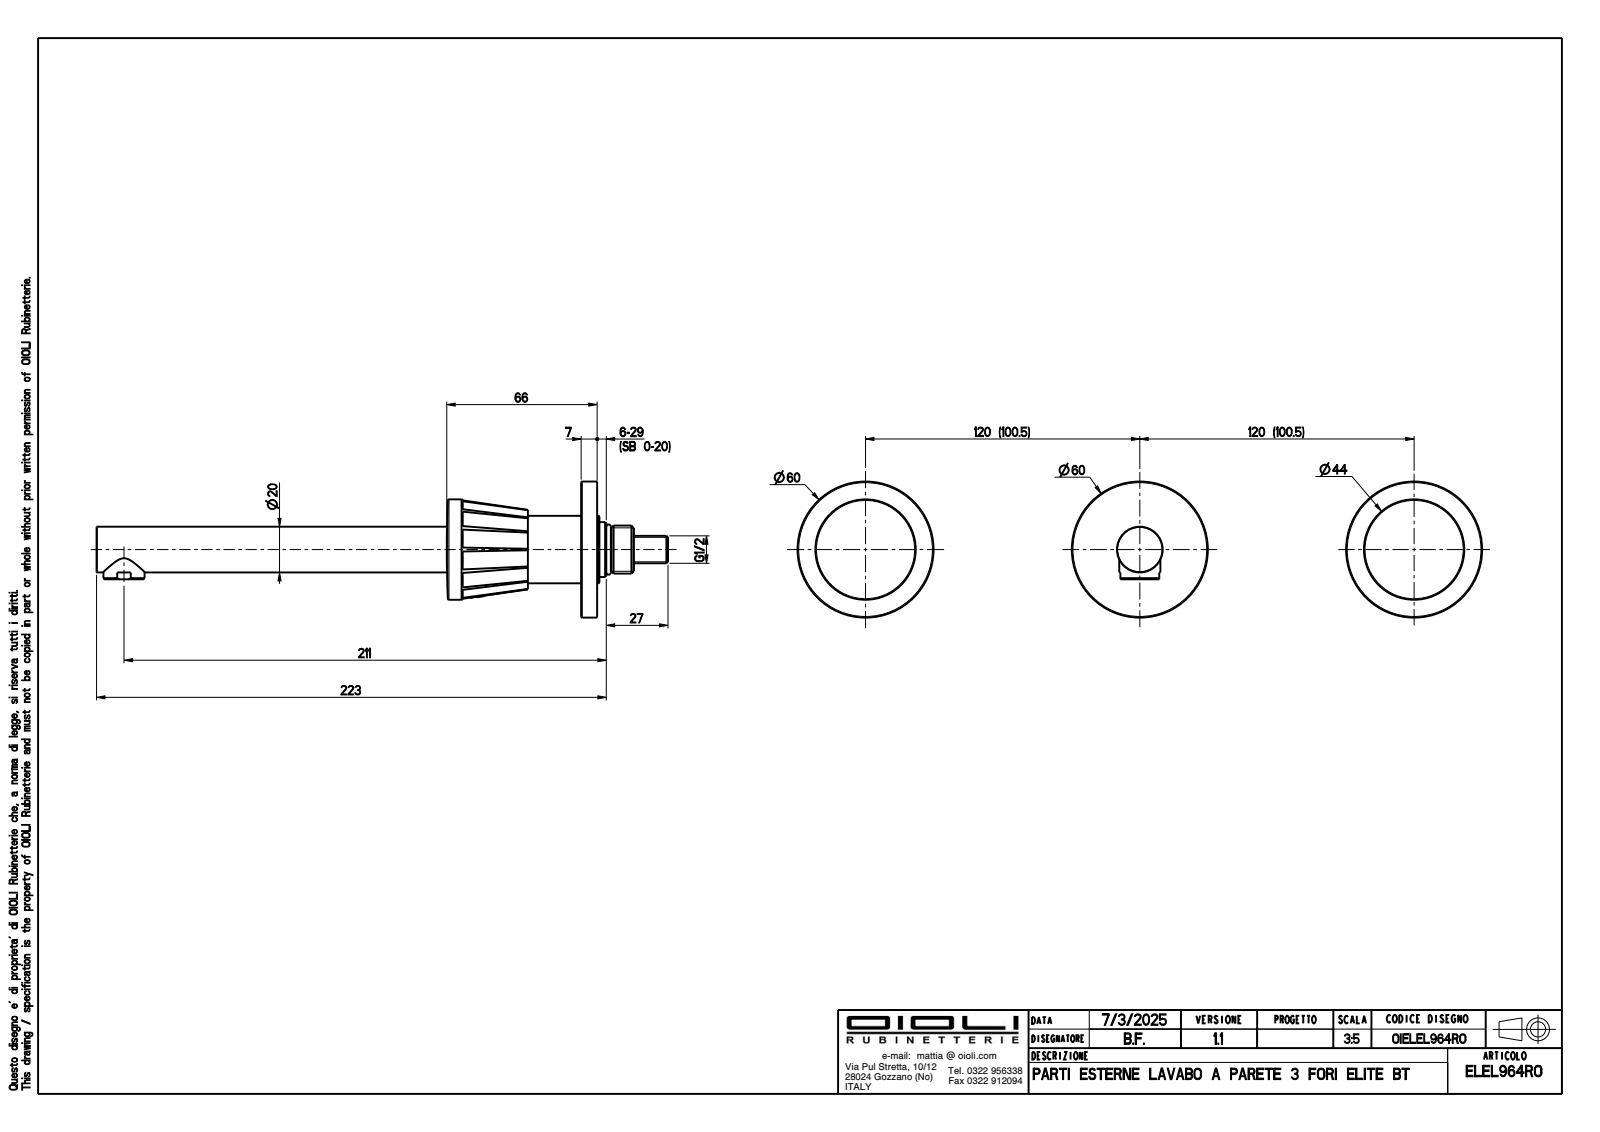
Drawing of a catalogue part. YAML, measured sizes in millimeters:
part_name: "OIBR00632; OIBR00950; OIBR00633; OIBR00689 (+6 more)"
step_written_by: "CREO PARAMETRIC BY PTC INC, 2024493 (CONFIG_CONTROL_DESIGN)"
units: millimeters
bodies: {solids: 14, faces: 618, planar: 266, cylindrical: 172, other: 180}
overall_size: [431.4, 299.5, 97.42]
volume: 105869
surface_area: 91834
round_holes:
  - {diameter: 4.2, count: 3}
  - {diameter: 14, count: 3}
  - {diameter: 4, count: 2}
  - {diameter: 5.3, count: 2}
  - {diameter: 6.5, count: 2}
  - {diameter: 7, count: 2}
  - {diameter: 15.5, count: 2}
  - {diameter: 23, count: 2}
  - {diameter: 27, count: 2}
  - {diameter: 30, count: 2}
  - {diameter: 33, count: 2}
  - {diameter: 57.3, count: 2}
round_bosses_or_shafts:
  - {diameter: 59.5, count: 3}
  - {diameter: 16.5, count: 3}
  - {diameter: 5, count: 3}
  - {diameter: 43.9, count: 2}
  - {diameter: 36, count: 2}
  - {diameter: 29.5, count: 2}
  - {diameter: 24, count: 2}
  - {diameter: 20, count: 1}
partial_cylinders:
  - {radius: 0.1, count: 20}
face_to_face_distances: [24.26, 2, 1.5, 19.64, 4.62, 21.64, 2.62, 21.14, 23.14, 25.76]
hole_center_spacings: [120, 120.09, 4.7, 151.75, 155.64, 192, 193.31, 240]
